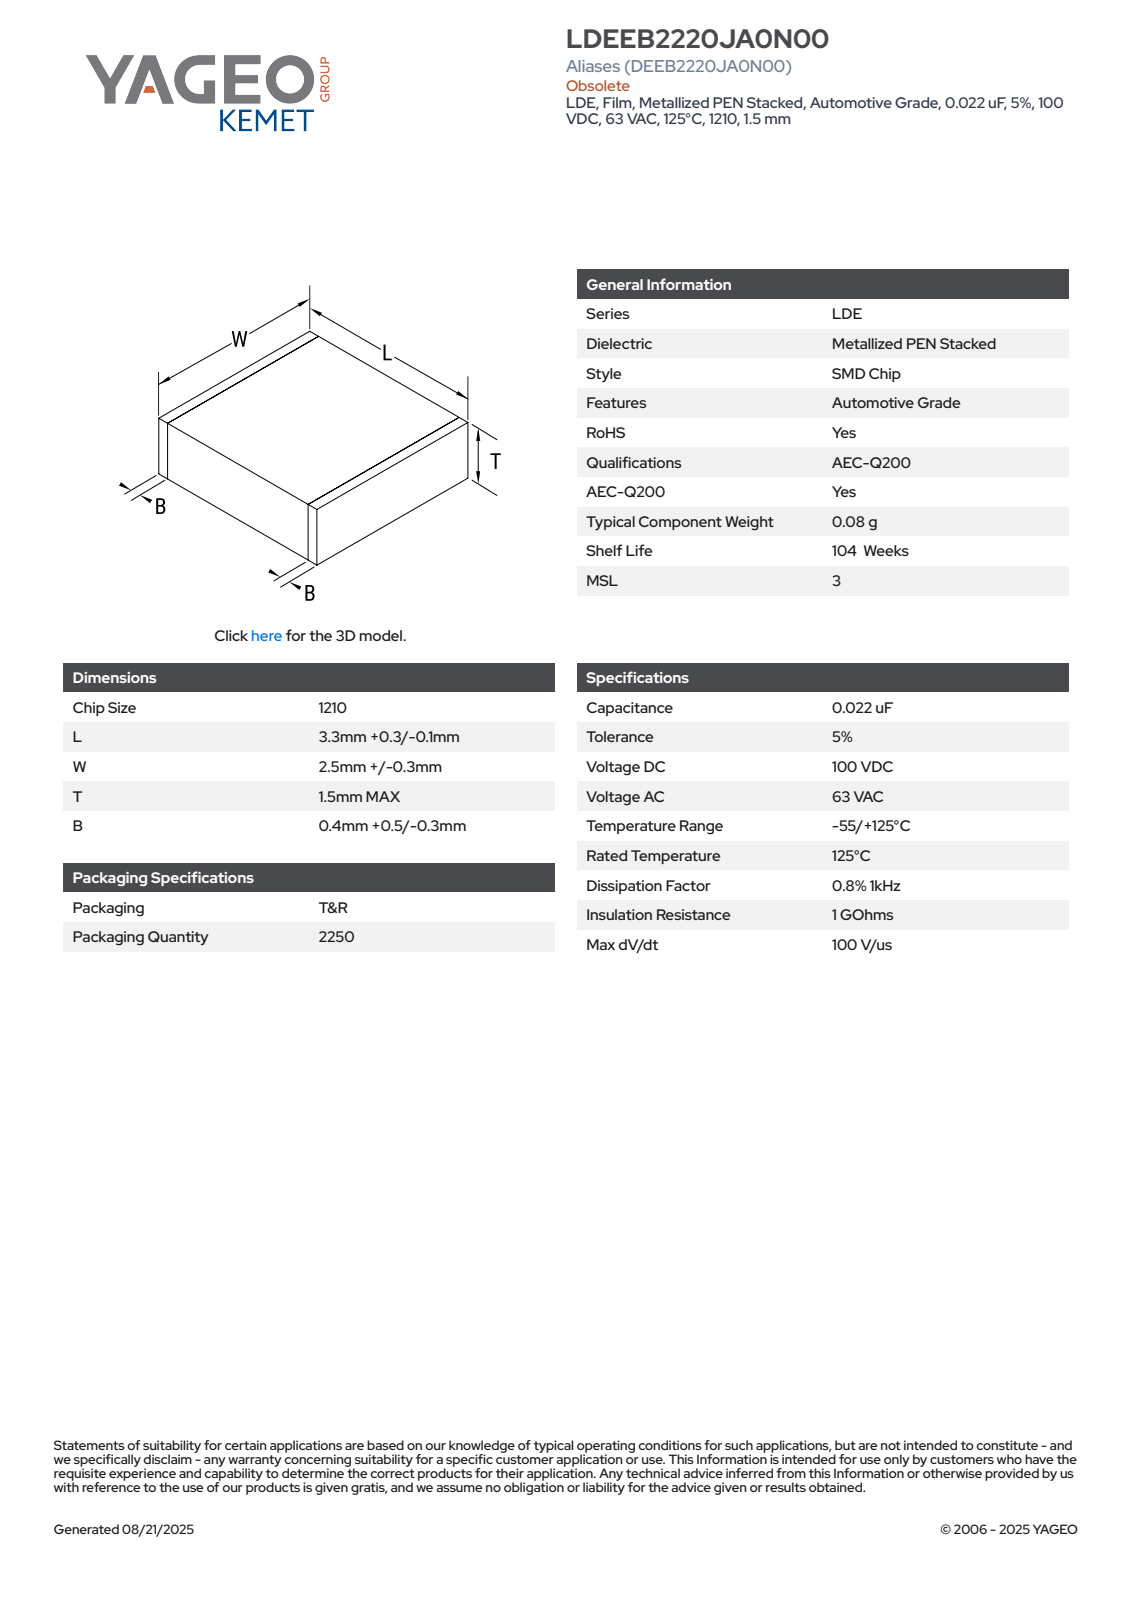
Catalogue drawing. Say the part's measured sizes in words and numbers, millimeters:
The part is named "CFS_LDELDB_1210_L3.6W2.8T1.5B0.9". Its 3-D file was written by "SolidWorks 2020 (AUTOMOTIVE_DESIGN)". It is 4 solids with 73 faces: 73 planar, 0 cylindrical and 0 other. Overall it measures 3.6 by 2.8 by 1.5 millimeters. Its volume is 15 cubic millimeters and its surface area 40 square millimeters. The main face-to-face distances are 1.48, 1.49, 3.6, 2.78, 2.79, 1.5, 2.8, 0.5, 3.1, 2.6.
